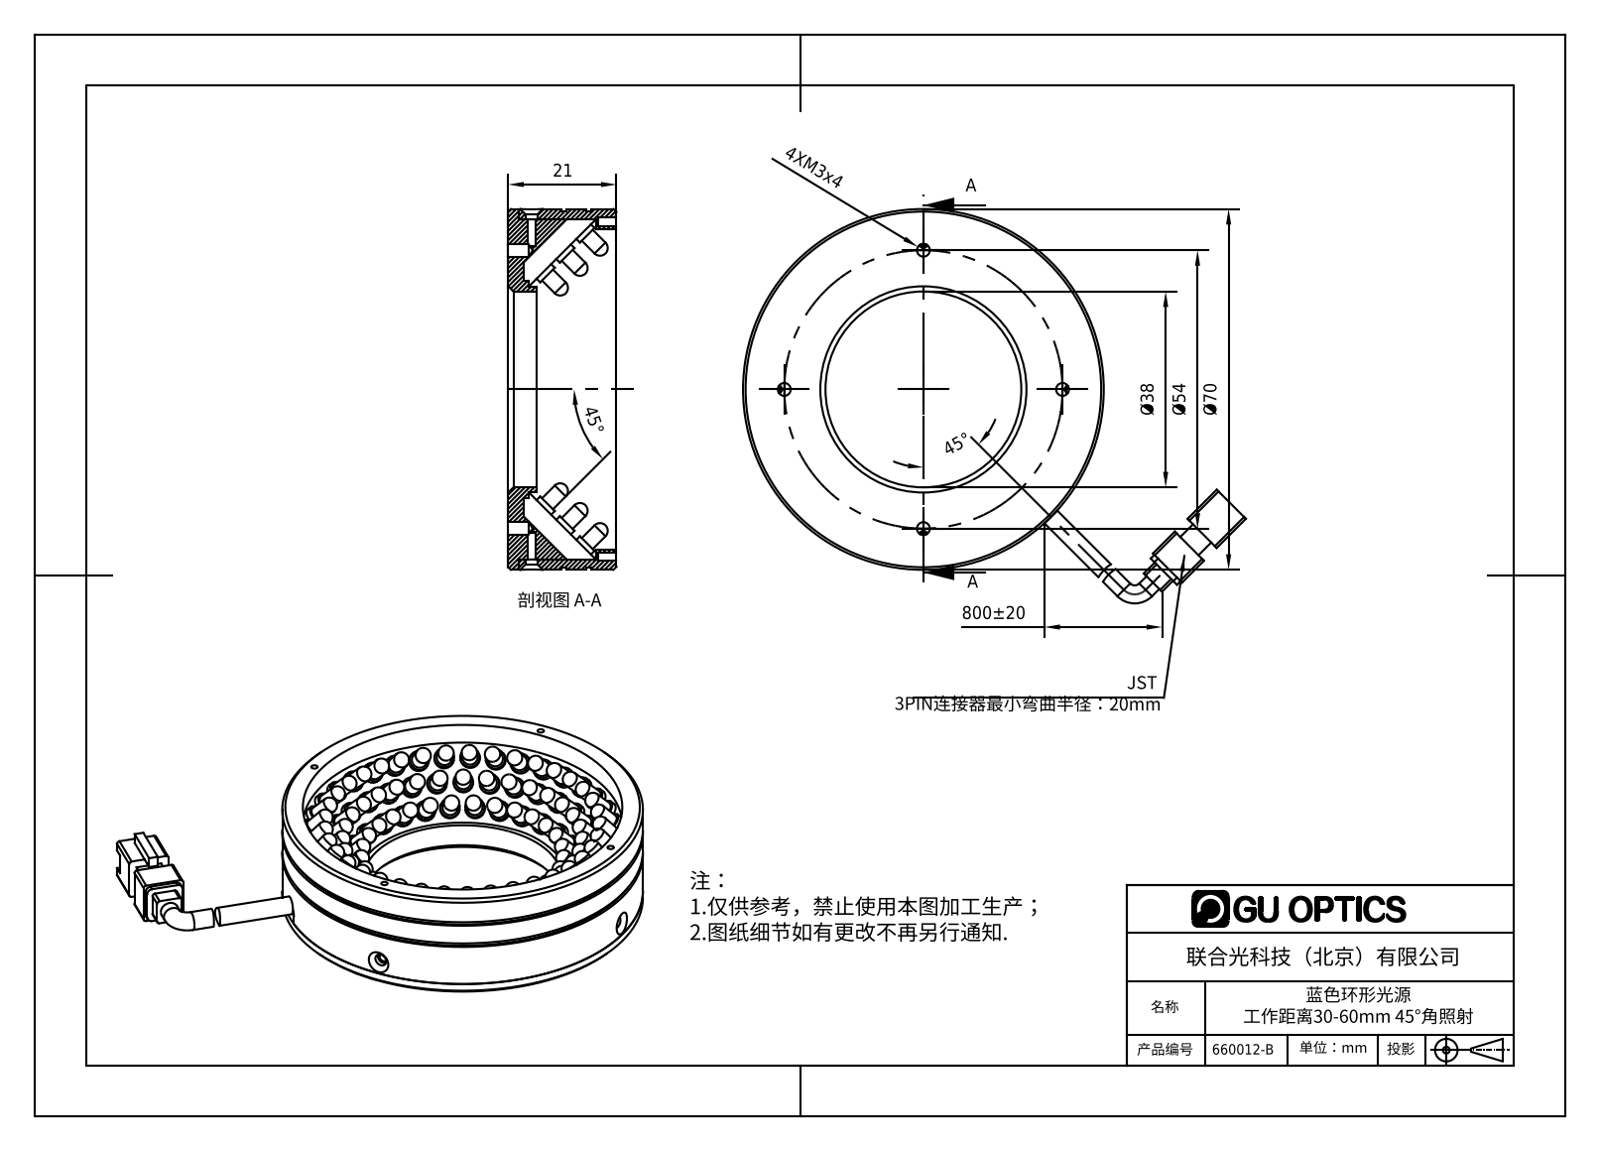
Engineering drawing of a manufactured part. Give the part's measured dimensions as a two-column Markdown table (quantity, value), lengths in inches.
| quantity | value |
| --- | --- |
| part name | 660012-B |
| STEP written by | SolidWorks 2016 (AUTOMOTIVE_DESIGN) |
| units | inches |
| bodies | 103 solids, 1900 faces (1251 planar, 494 cylindrical, 155 other) |
| overall size | 3.842 × 3.013 × 0.827 |
| volume | 1.814 in³ |
| surface area | 54.48 in² |
| round holes (diameter × count) | 0.049 × 4, 0.098 × 4, 0.118 × 3, 0.063 × 2, 0.094 × 2, 1.496 × 1, 2.441 × 1 |
| round bosses / shafts (diameter × count) | 0.15 × 98, 0.118 × 97, 0.138 × 2, 2.756 × 1, 2.717 × 1, 2.598 × 1, 1.654 × 1, 1.575 × 1 |
| partial cylindrical surfaces (radius × count) | 0.02 × 8, 0.039 × 4, 0.065 × 1, 0.197 × 1 |
| main face-to-face distances | 0.039, 0.079, 0.118, 0.748, 0.157, 0.827, 0.669, 0.709, 0.02, 0.551 |
| hole center spacings | 1.663, 0.217, 1.063, 1.28, 1.503, 1.809, 2.343, 2.126 |
